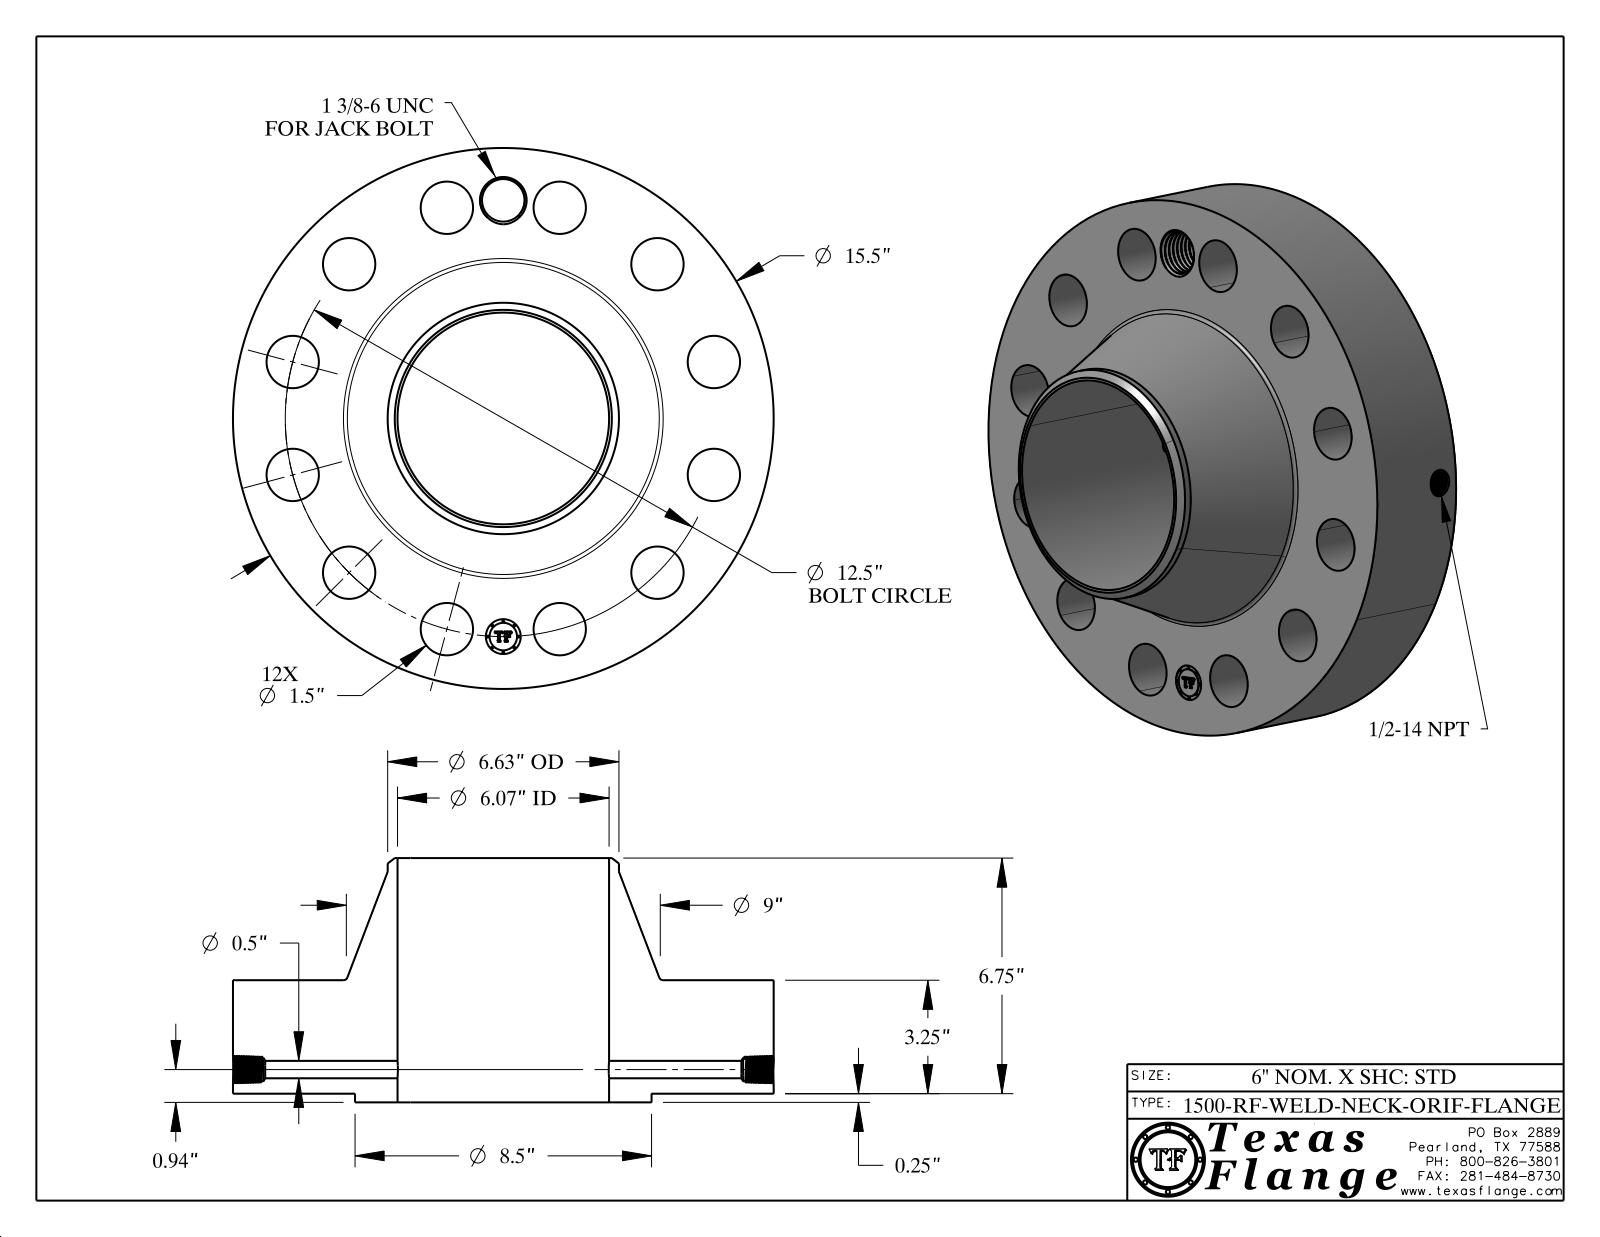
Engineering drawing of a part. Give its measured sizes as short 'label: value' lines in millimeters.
name: 1500-RF-WELD-NECK
written by: CATIA V5 STEP AP214 (AUTOMOTIVE_DESIGN)
unit: mm
bodies: 1 solid, 804 faces (369 planar, 111 cylindrical, 324 other)
size: 393.7 × 393.7 × 177.8
volume: 8 410 000 mm³; area: 549 100 mm²
holes: 12× ⌀38.1, 1× ⌀12.7, 1× ⌀17.1, 1× ⌀25.4, 1× ⌀31, 1× ⌀154.1
bosses: 8× ⌀1.5, 1× ⌀393.7, 1× ⌀215.9, 1× ⌀168.4, 1× ⌀20
face distances: 82.6, 88.9, 6.4, 177.8, 171.5, 88.5, 82.2, 0.4, 89.3, 7.6
hole spacings: 158.8, 306.7, 82.2, 224.5, 275, 317.5, 41.4, 82.2
